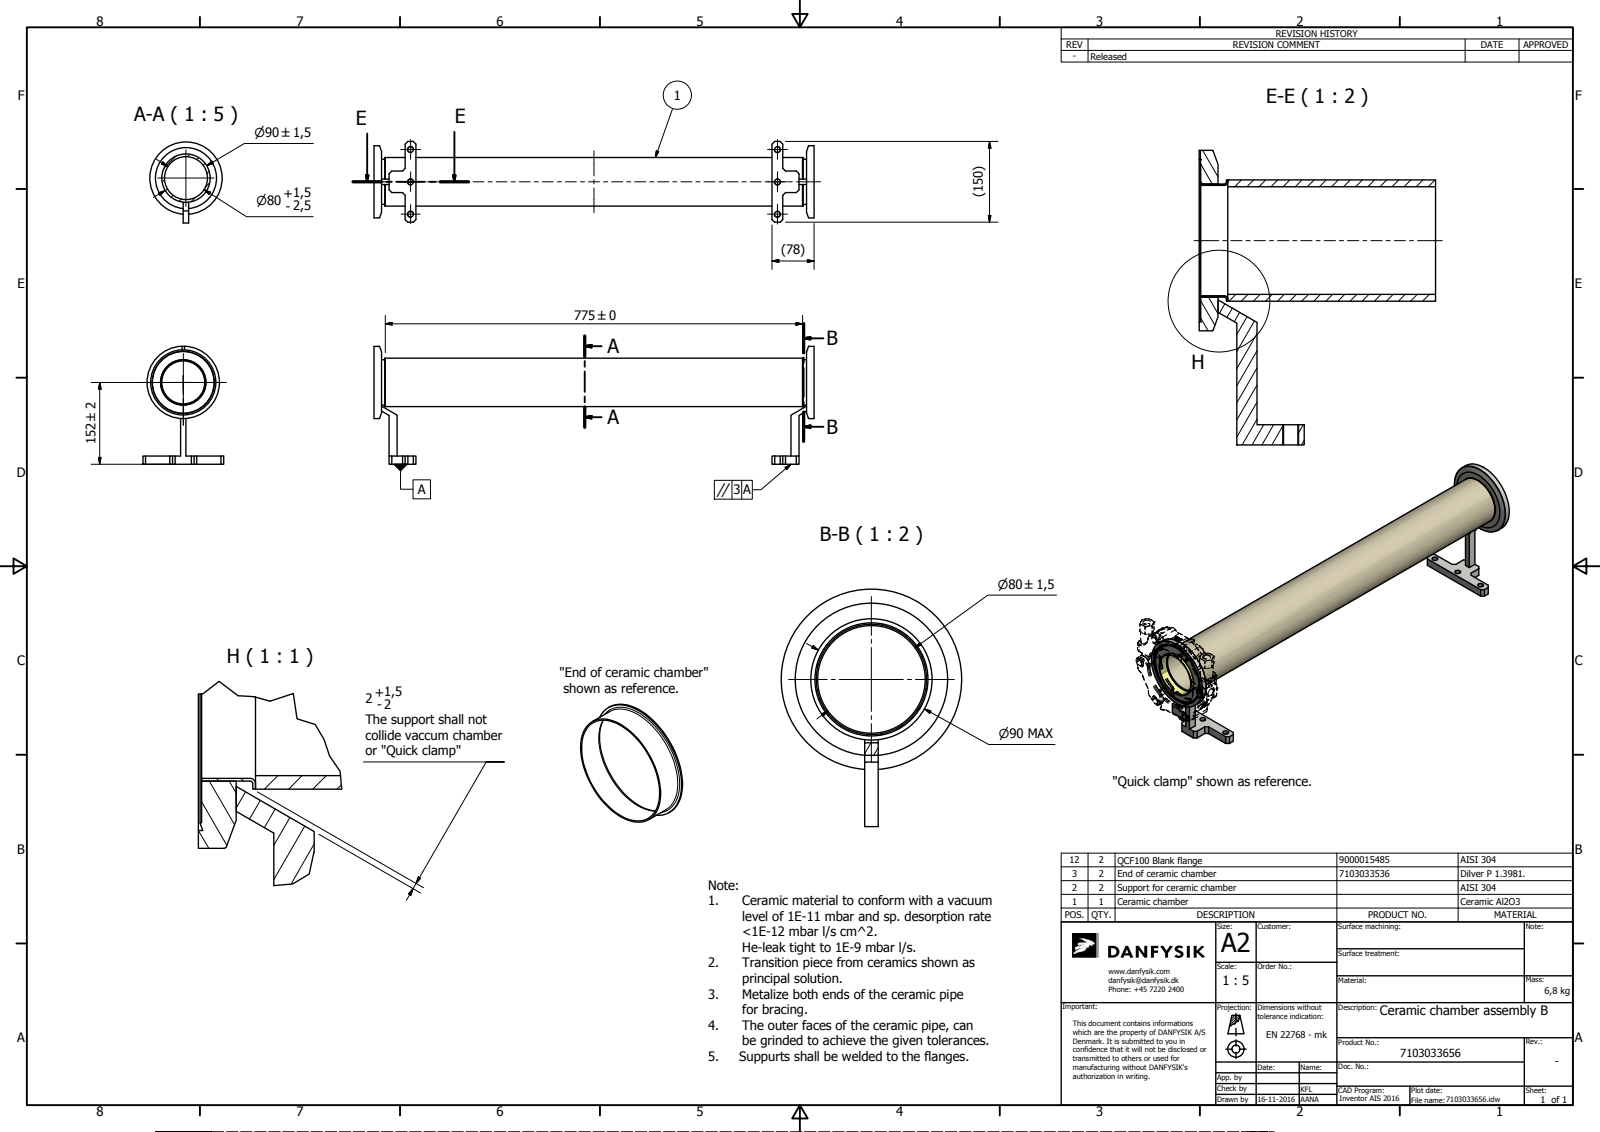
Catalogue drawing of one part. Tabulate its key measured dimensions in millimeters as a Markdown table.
| quantity | value |
| --- | --- |
| part name | 7103033538; 7103033536; 7103033537; 7103033540 (+3 more) |
| STEP written by | Autodesk Inventor 2016 (AUTOMOTIVE_DESIGN) |
| units | millimeters |
| bodies | 7 solids, 96 faces (62 planar, 22 cylindrical, 12 other) |
| overall size | 817.05 × 218.74 × 150 |
| volume | 1 399 000 mm³ |
| surface area | 531 623 mm² |
| round holes (diameter × count) | 10.65 × 6, 80 × 1, 82 × 1, 84 × 1, 120.7 × 1 |
| round bosses / shafts (diameter × count) | 134 × 1, 90 × 1 |
| partial cylindrical surfaces (radius × count) | 3 × 2 |
| main face-to-face distances | 15, 12.8, 801.84, 14, 789.04, 737.84, 20, 56.8, 1.2, 803.04 |
| hole center spacings | 60, 683.68, 681.04, 120, 691.53 |
